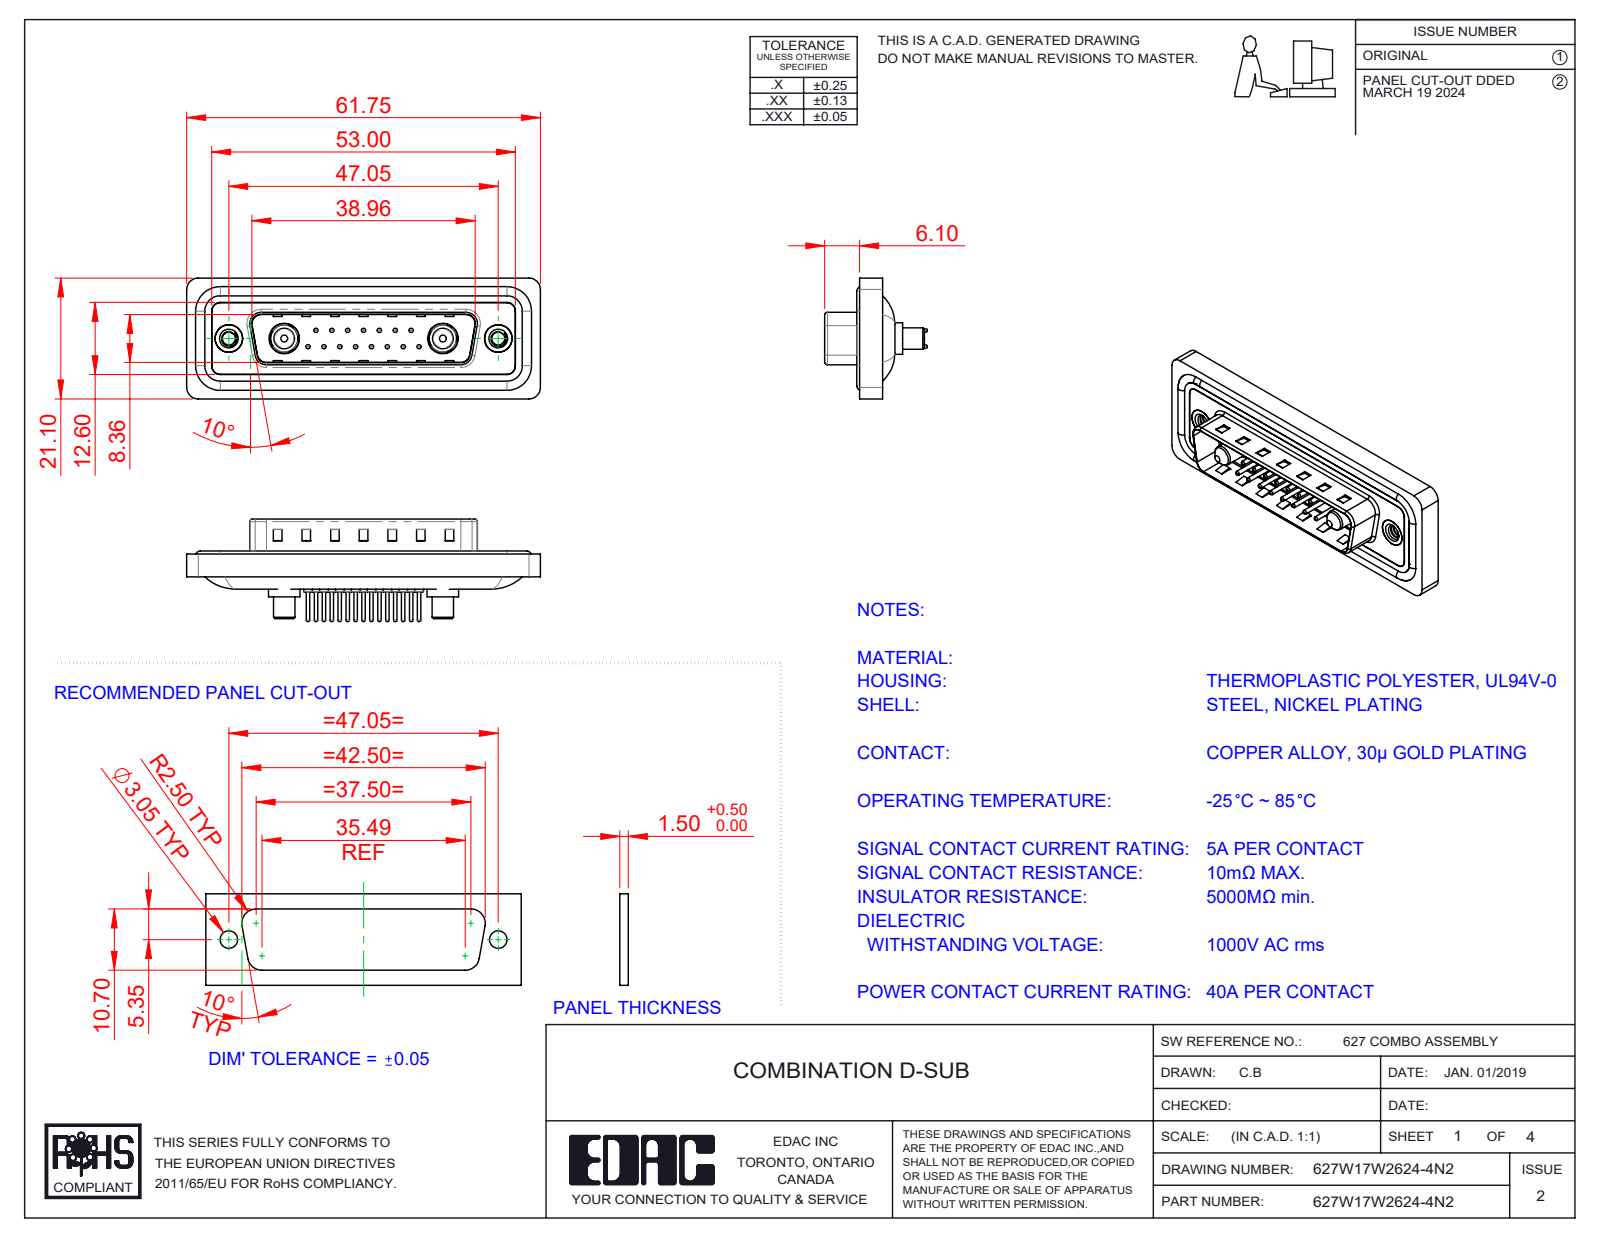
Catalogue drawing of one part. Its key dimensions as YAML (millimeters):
part_name: "627Combo Contact Row 1_24; 627Combo Housing_17W2; Power Pin_40A S; 627Combo Waterproof Housing_25 Contacts (+5 more)"
step_written_by: "SolidWorks 2023 (CONFIG_CONTROL_DESIGN)"
units: millimeters
bodies: {solids: 26, faces: 1116, planar: 334, cylindrical: 436, other: 346}
overall_size: [61.75, 21.1, 17.9]
volume: 7303
surface_area: 11936
round_holes:
  - {diameter: 0.75, count: 15}
  - {diameter: 1.6, count: 15}
  - {diameter: 2, count: 15}
  - {diameter: 2.26, count: 2}
  - {diameter: 4, count: 2}
  - {diameter: 4.8, count: 2}
  - {diameter: 4.85, count: 2}
  - {diameter: 5, count: 2}
  - {diameter: 5.3, count: 2}
round_bosses_or_shafts:
  - {diameter: 1.5, count: 15}
  - {diameter: 0.6, count: 15}
  - {diameter: 1.6, count: 4}
  - {diameter: 5.5, count: 2}
  - {diameter: 5.2, count: 2}
  - {diameter: 4.9, count: 2}
  - {diameter: 4.75, count: 2}
  - {diameter: 3.75, count: 2}
partial_cylinders:
  - {radius: 1.5, count: 22}
  - {radius: 2, count: 18}
  - {radius: 0.5, count: 8}
  - {radius: 1.6, count: 8}
  - {radius: 0.25, count: 4}
  - {radius: 0.6, count: 4}
  - {radius: 0.65, count: 4}
  - {radius: 0.9, count: 4}
face_to_face_distances: [0.4, 1.5, 1.1, 1.6, 0.5, 3.1, 2.9, 0.82, 9.58, 4.1]
hole_center_spacings: [3.16, 2.77, 5.54, 8.31, 5.04, 7.49, 11.08, 5.03]
